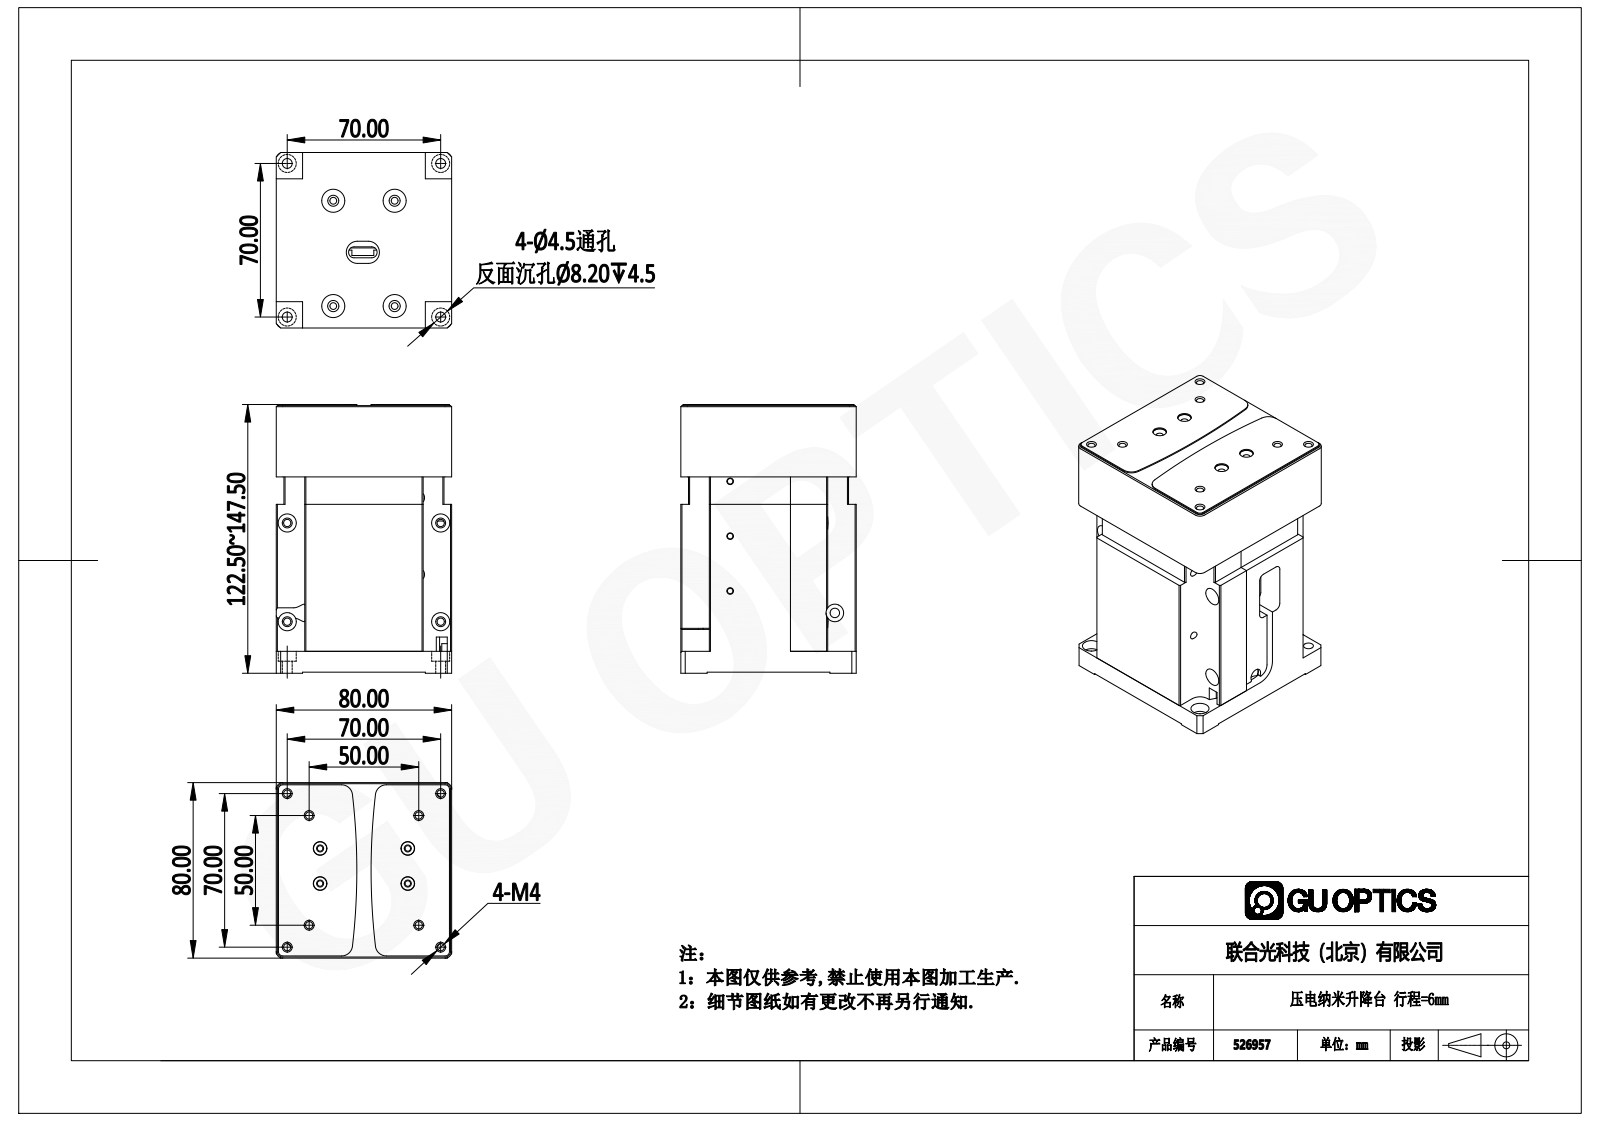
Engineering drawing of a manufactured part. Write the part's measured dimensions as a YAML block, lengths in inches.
part_name: "526957"
step_written_by: "SolidWorks 2020 (CONFIG_CONTROL_DESIGN)"
units: inches
bodies: {solids: 10, faces: 1172, planar: 562, cylindrical: 375, other: 235}
overall_size: [4.823, 3.15, 3.15]
volume: 32.98
surface_area: 244.9
round_holes:
  - {diameter: 0.13, count: 25}
  - {diameter: 0.325, count: 20}
  - {diameter: 0.169, count: 17}
  - {diameter: 0.236, count: 12}
  - {diameter: 0.098, count: 9}
  - {diameter: 0.177, count: 8}
  - {diameter: 0.126, count: 4}
  - {diameter: 0.201, count: 4}
  - {diameter: 0.244, count: 4}
  - {diameter: 0.315, count: 4}
  - {diameter: 0.413, count: 4}
  - {diameter: 0.063, count: 3}
round_bosses_or_shafts:
  - {diameter: 0.118, count: 20}
partial_cylinders:
  - {radius: 0.197, count: 46}
  - {radius: 0.098, count: 8}
  - {radius: 0.118, count: 6}
  - {radius: 0.079, count: 4}
  - {radius: 0.394, count: 4}
  - {radius: 0.02, count: 2}
  - {radius: 0.059, count: 2}
  - {radius: 0.122, count: 2}
face_to_face_distances: [0.02, 3.15, 0.374, 0.394, 1.26, 0.335, 1.969, 0.709, 1.181, 0.728]
hole_center_spacings: [0.984, 1.969, 1.075, 1.614, 2.395, 2.756, 0.433, 1.28]
